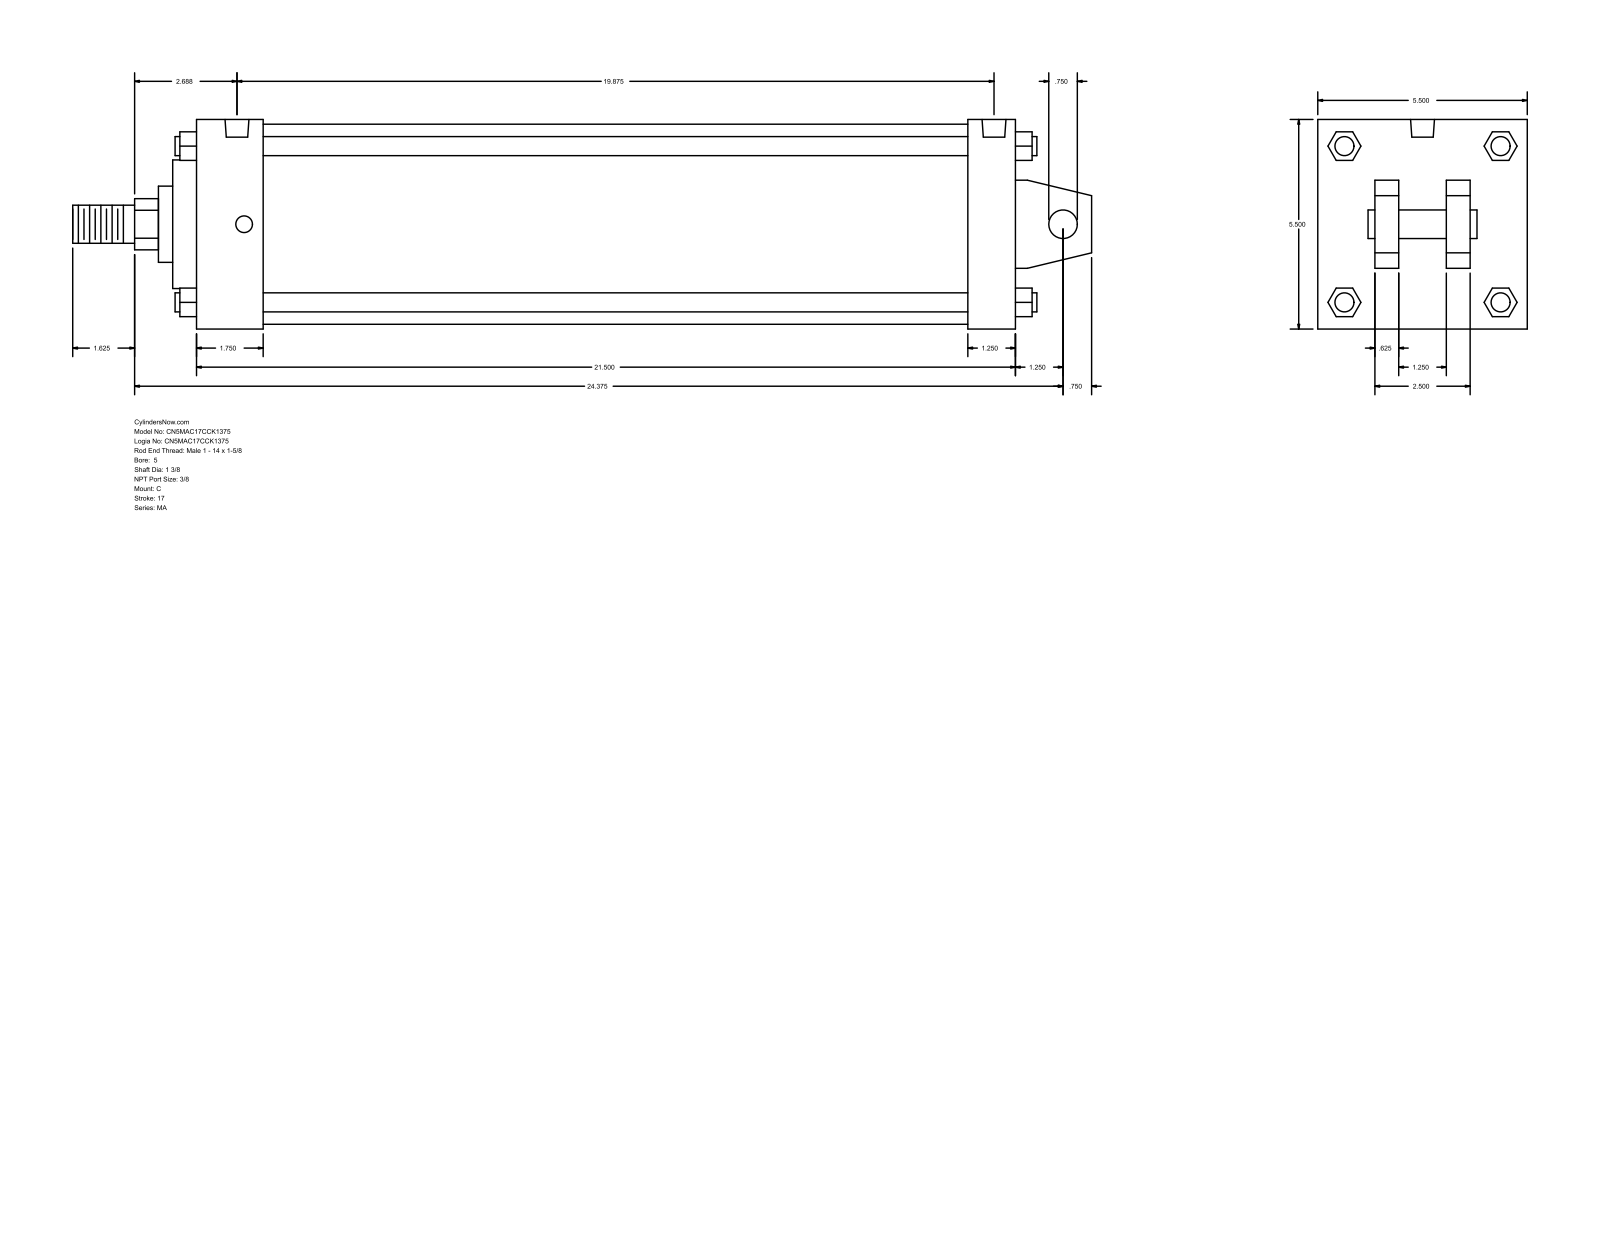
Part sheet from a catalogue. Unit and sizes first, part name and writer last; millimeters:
Units: millimetres
Overall size (bounding box): 679.45 × 139.7 × 139.7
Round holes (diameter × count): ⌀11.11 ×4, ⌀15.93 ×2
Round bosses / shafts (diameter × count): ⌀12.7 ×4, ⌀133.35 ×1, ⌀85.72 ×1, ⌀50.8 ×1, ⌀34.92 ×1, ⌀25.4 ×1, ⌀19.05 ×1
Partial cylindrical surfaces — rounded edges, fillets, slot ends (radius × count): R17.06 ×1
Main face-to-face distances: 139.7, 546.11, 15.87, 31.76, 514.35, 44.45, 469.9, 501.66, 53.97, 38.1
Hole centre spacings: 495.3, 4.76, 4.77, 500.06, 500.07, 504.83
Bodies: 0 solids, 141 faces (109 planar, 32 cylindrical, 0 other)
Part name (STEP PRODUCT): MA_C__0500_1.375
STEP written by: GSSL Pune (CONFIG_CONTROL_DESIGN)
